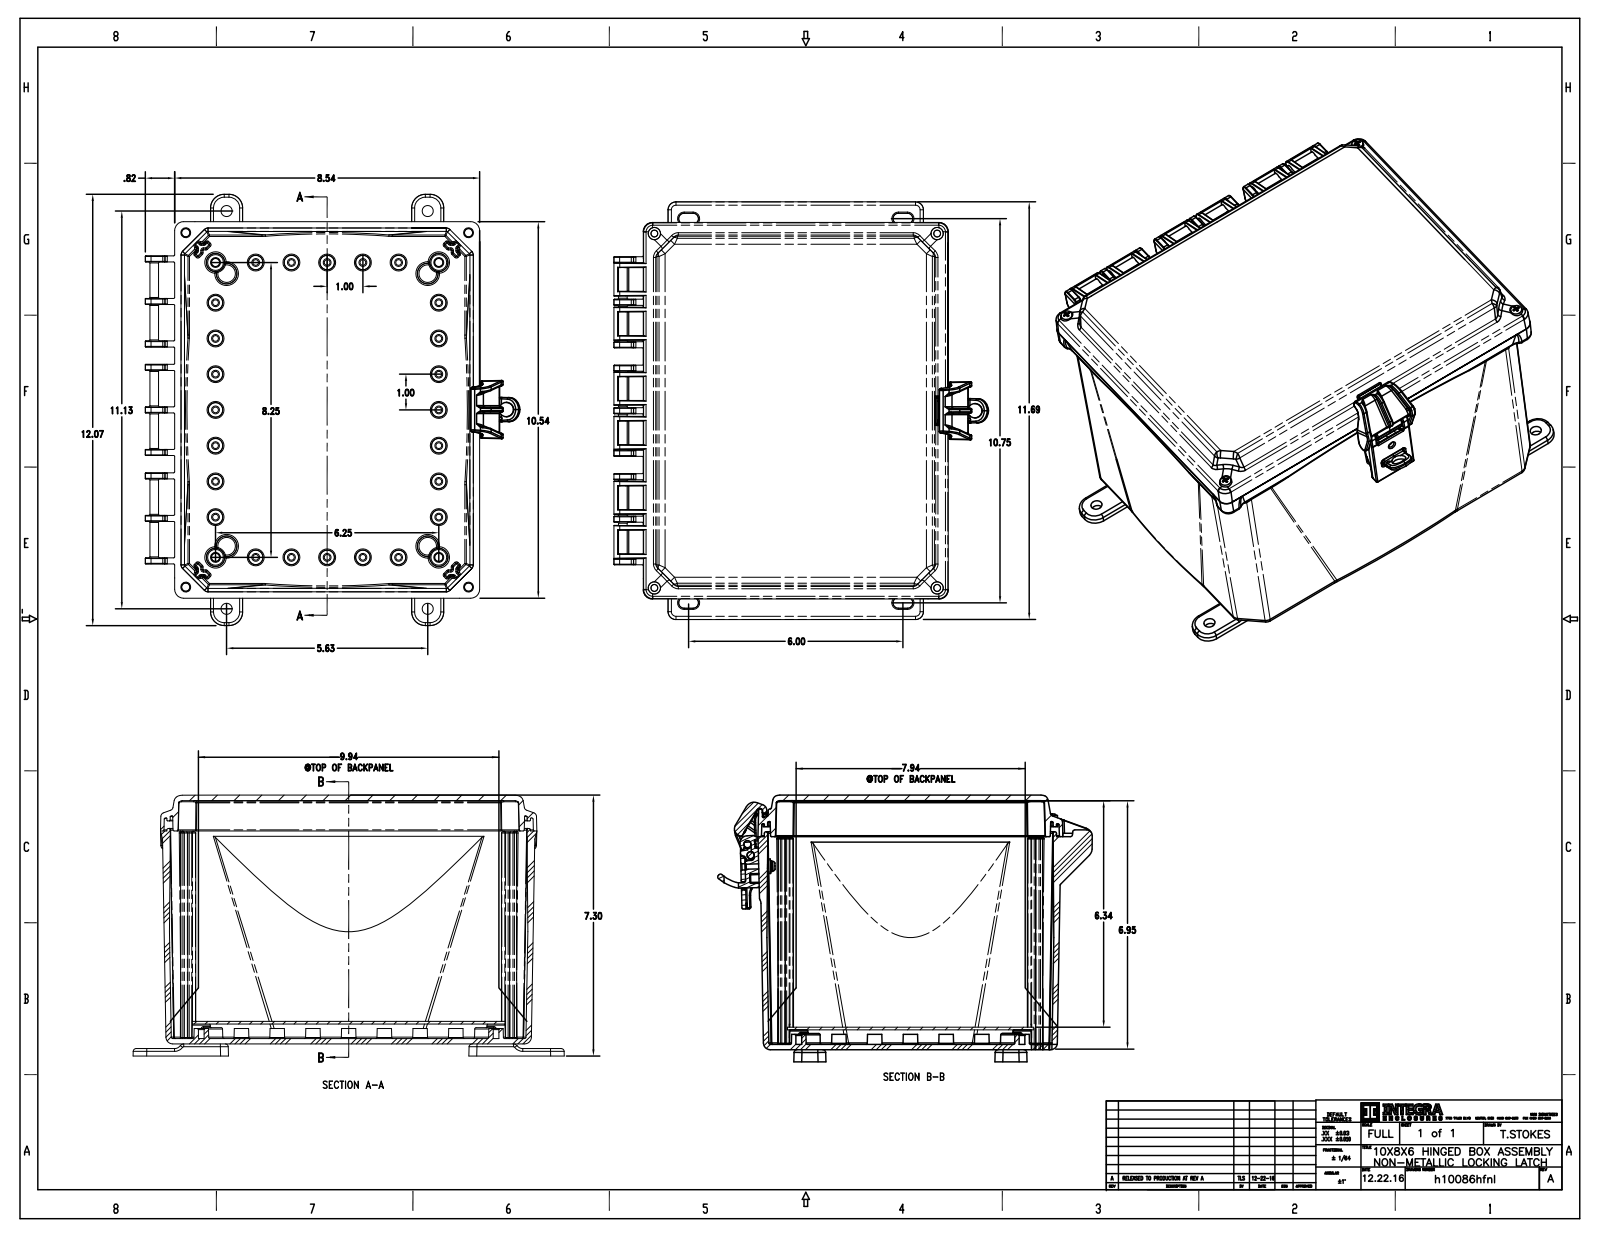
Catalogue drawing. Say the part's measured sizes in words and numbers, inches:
The part is named "H1086BH; 9912525-80-10; 9912521-80-10; H1086BH_ASM (+8 more)". Its 3-D file was written by "CREO PARAMETRIC BY PTC INC, 2016050 (CONFIG_CONTROL_DESIGN)". It is 32 solids with 6929 faces: 2793 planar, 2196 cylindrical and 1940 other. Overall it measures 11.69 by 10.487 by 7.465 inches. Its volume is 78.43 cubic inches and its surface area 1 084 square inches. Round holes: 24 of diameter 0.16, 8 of diameter 0.19, 4 of diameter 0.201, 2 of diameter 0.116, 2 of diameter 0.125, 1 of diameter 0.08, 1 of diameter 0.14, 1 of diameter 0.175, 1 of diameter 0.21, 1 of diameter 0.33, 1 of diameter 0.35, 1 of diameter 0.4. Round bosses or shafts: 12 of diameter 0.25, 8 of diameter 0.3, 8 of diameter 0.298, 8 of diameter 0.29, 8 of diameter 0.26, 8 of diameter 0.258, 4 of diameter 0.375, 4 of diameter 0.372. Partial cylindrical surfaces (rounded edges, fillets, slot ends): 430 of radius 0.03, 179 of radius 0.02, 104 of radius 0.015, 49 of radius 0.005, 48 of radius 0.01, 42 of radius 0.04, 42 of radius 0.09, 28 of radius 0.1. The main face-to-face distances are 0.15, 0.49, 5.81, 0.12, 5.96, 0.392, 0.27, 6.08, 0.34, 0.098. The hole center spacings are 1, 2, 3, 6.33, 6.563, 2.128, 2.404, 3.073.
